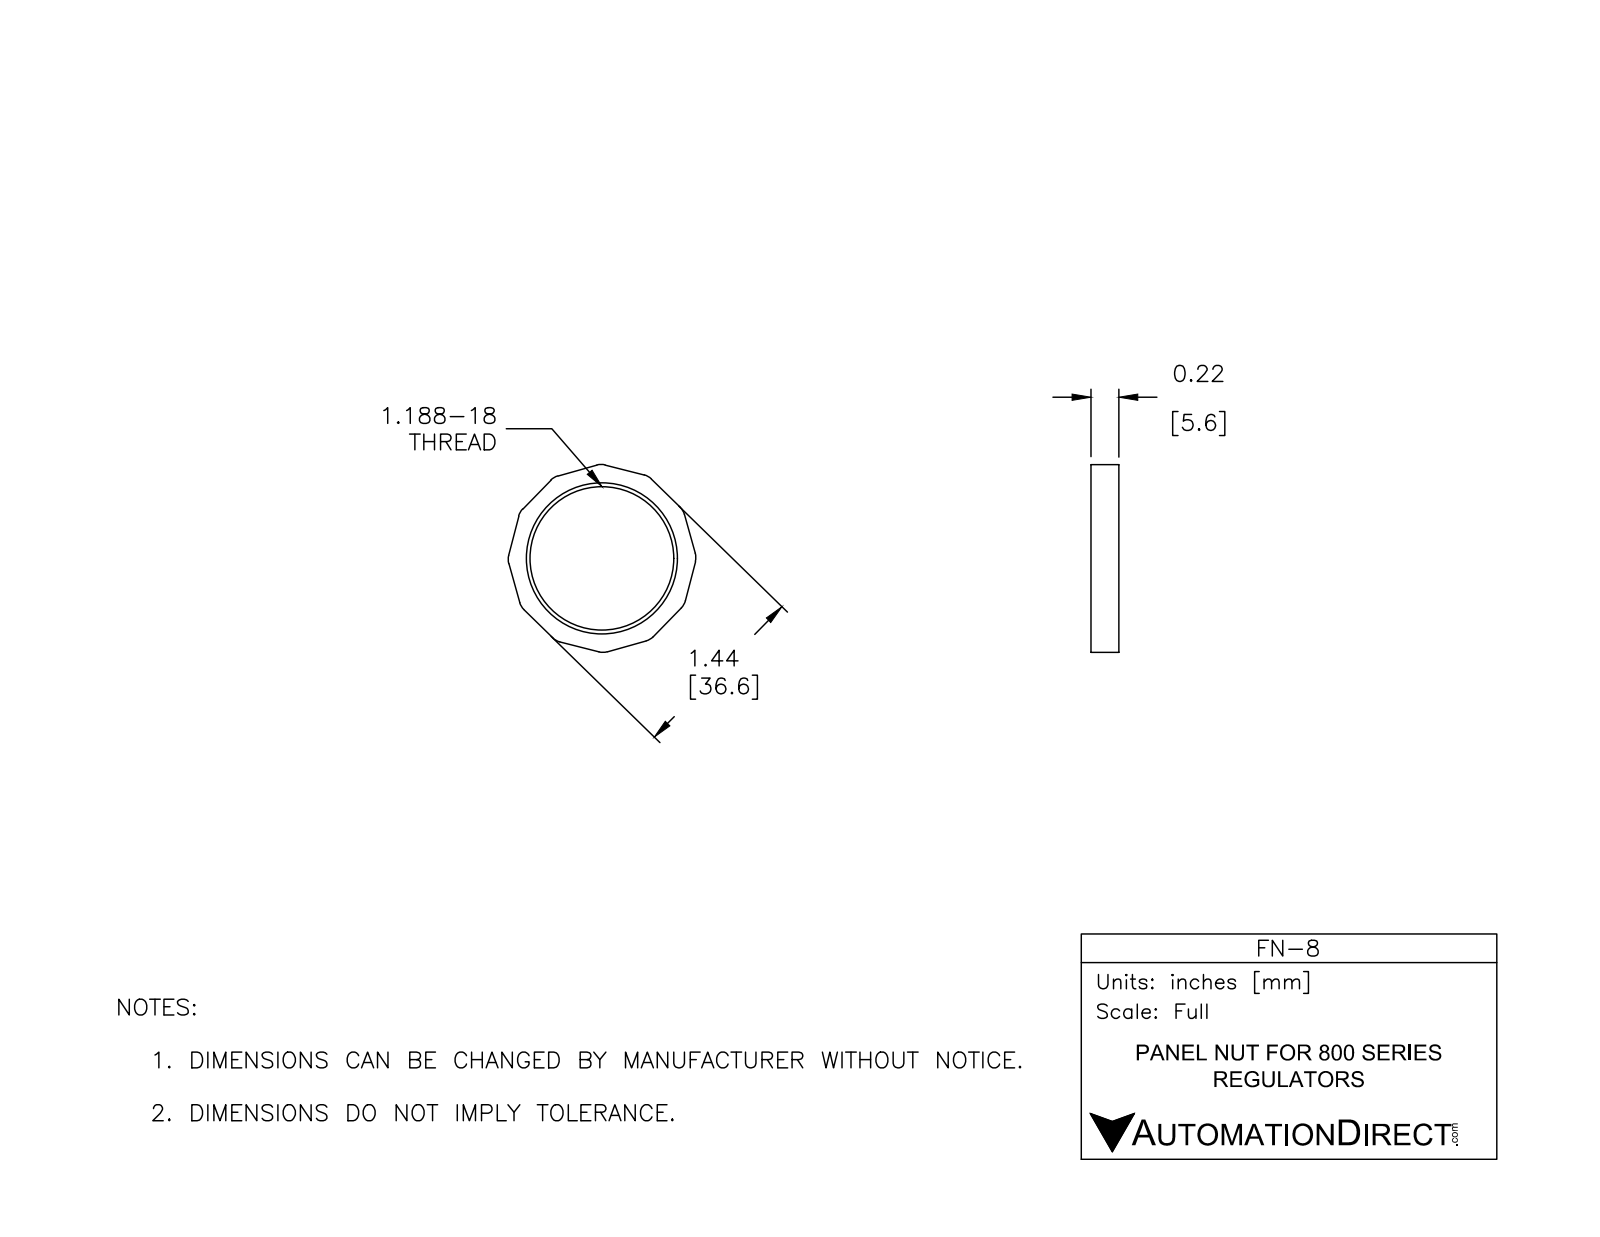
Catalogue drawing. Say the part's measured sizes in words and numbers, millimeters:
The part is named "739040". Its 3-D file was written by "Autodesk Inventor 2014 (AUTOMOTIVE_DESIGN)". It is 1 solid with 29 faces: 14 planar, 13 cylindrical and 2 other. Overall it measures 37.64 by 37.64 by 5.59 millimeters. Its volume is 2 317 cubic millimeters and its surface area 1 929 square millimeters. Round holes: 1 of diameter 28.78. Partial cylindrical surfaces (rounded edges, fillets, slot ends): 12 of radius 3.17. The main face-to-face distances are 5.59, 36.58.
